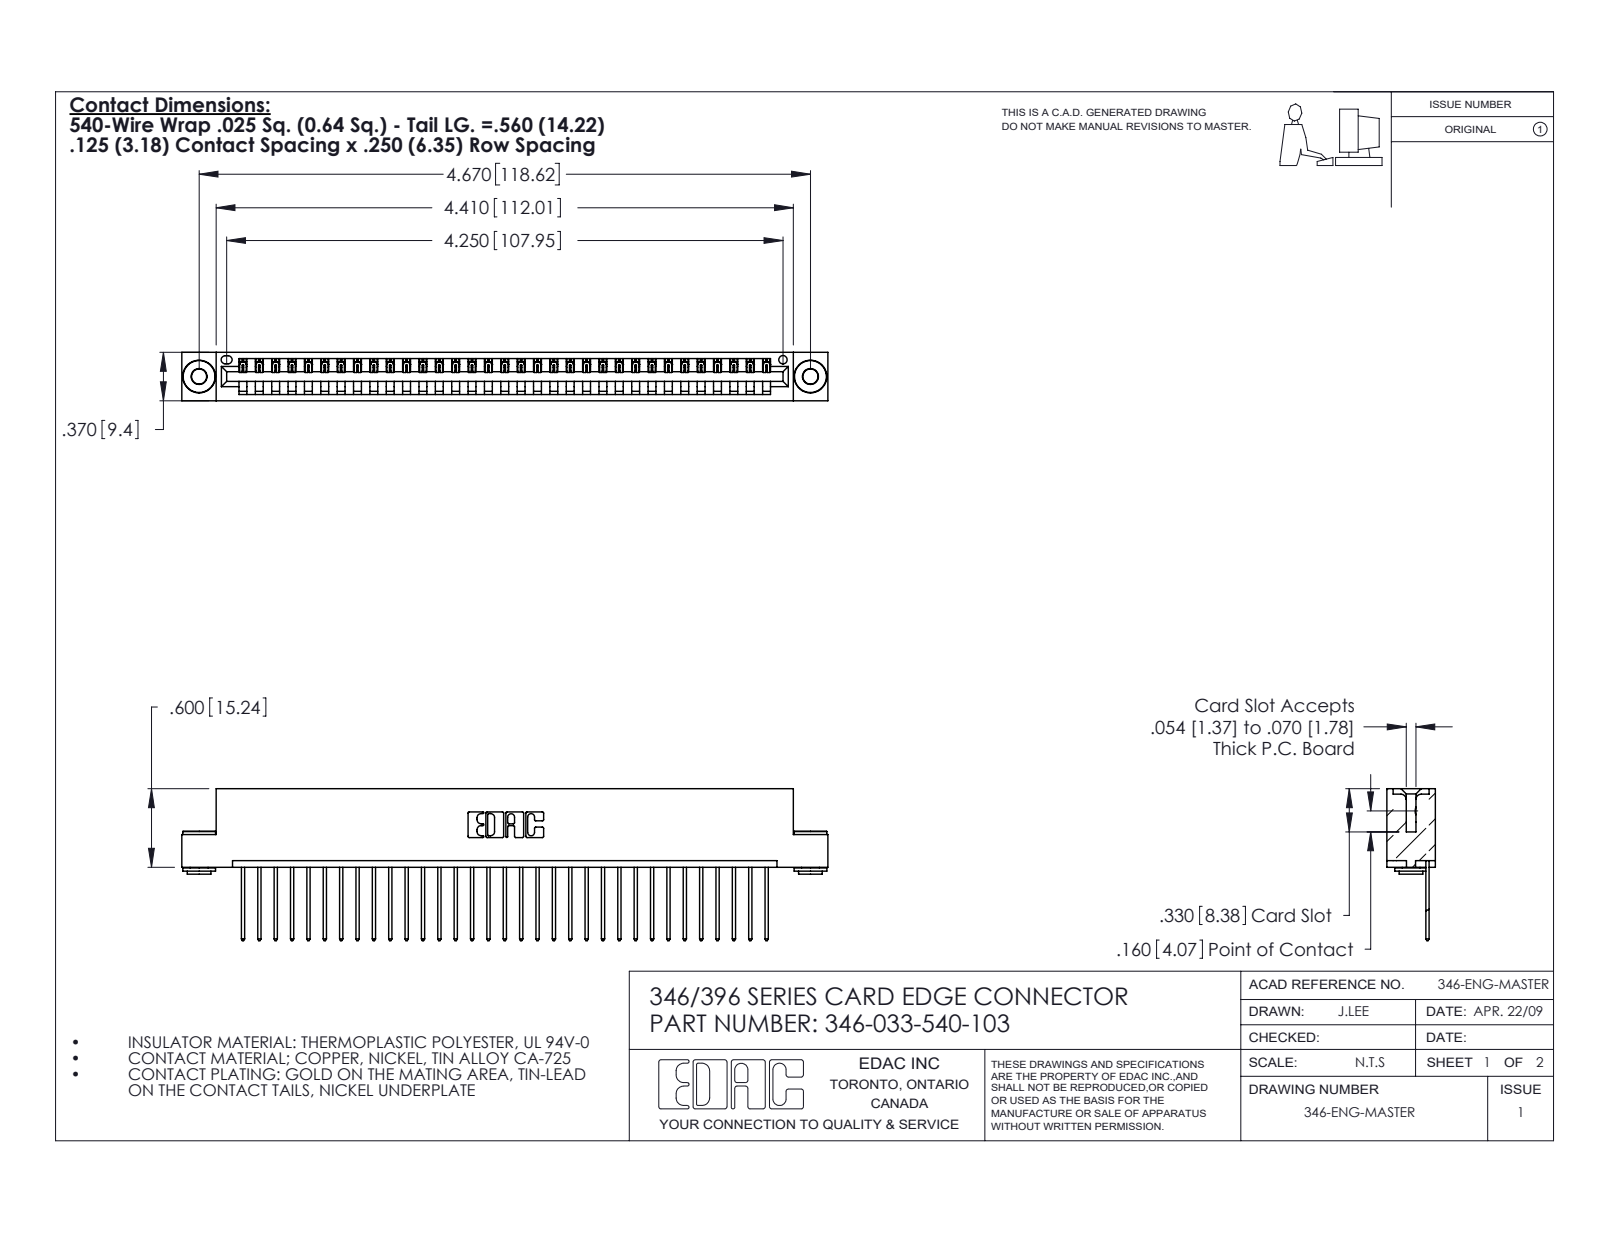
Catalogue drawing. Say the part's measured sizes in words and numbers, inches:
The part is named "345-292-001_345-293-140; 345-250-002_345-250-002-102; 346 Part_Flush Mounting Lugs - 0.156 Dia-TH; 346-033-540-103". Its 3-D file was written by "SolidWorks 2020 (CONFIG_CONTROL_DESIGN)". It is 36 solids with 2088 faces: 1420 planar, 660 cylindrical and 8 other. Overall it measures 4.935 by 1.16 by 0.37 inches. Its volume is 0.731 cubic inches and its surface area 23.96 square inches. Round holes: 2 of diameter 0.116, 2 of diameter 0.156, 1 of diameter 0.064. Round bosses or shafts: 2 of diameter 0.25, 2 of diameter 0.18, 2 of diameter 0.136. Partial cylindrical surfaces (rounded edges, fillets, slot ends): 66 of radius 0.006, 66 of radius 0.01, 22 of radius 0.01, 6 of radius 0.007, 6 of radius 0.031, 3 of radius 0.026, 2 of radius 0.031, 2 of radius 0.04. The main face-to-face distances are 0.048, 0.322, 0.37, 0.25, 0.025, 0.072, 0.298, 0.148, 0.222, 0.1. The hole center spacings are 0.246, 4.462, 4.67.
